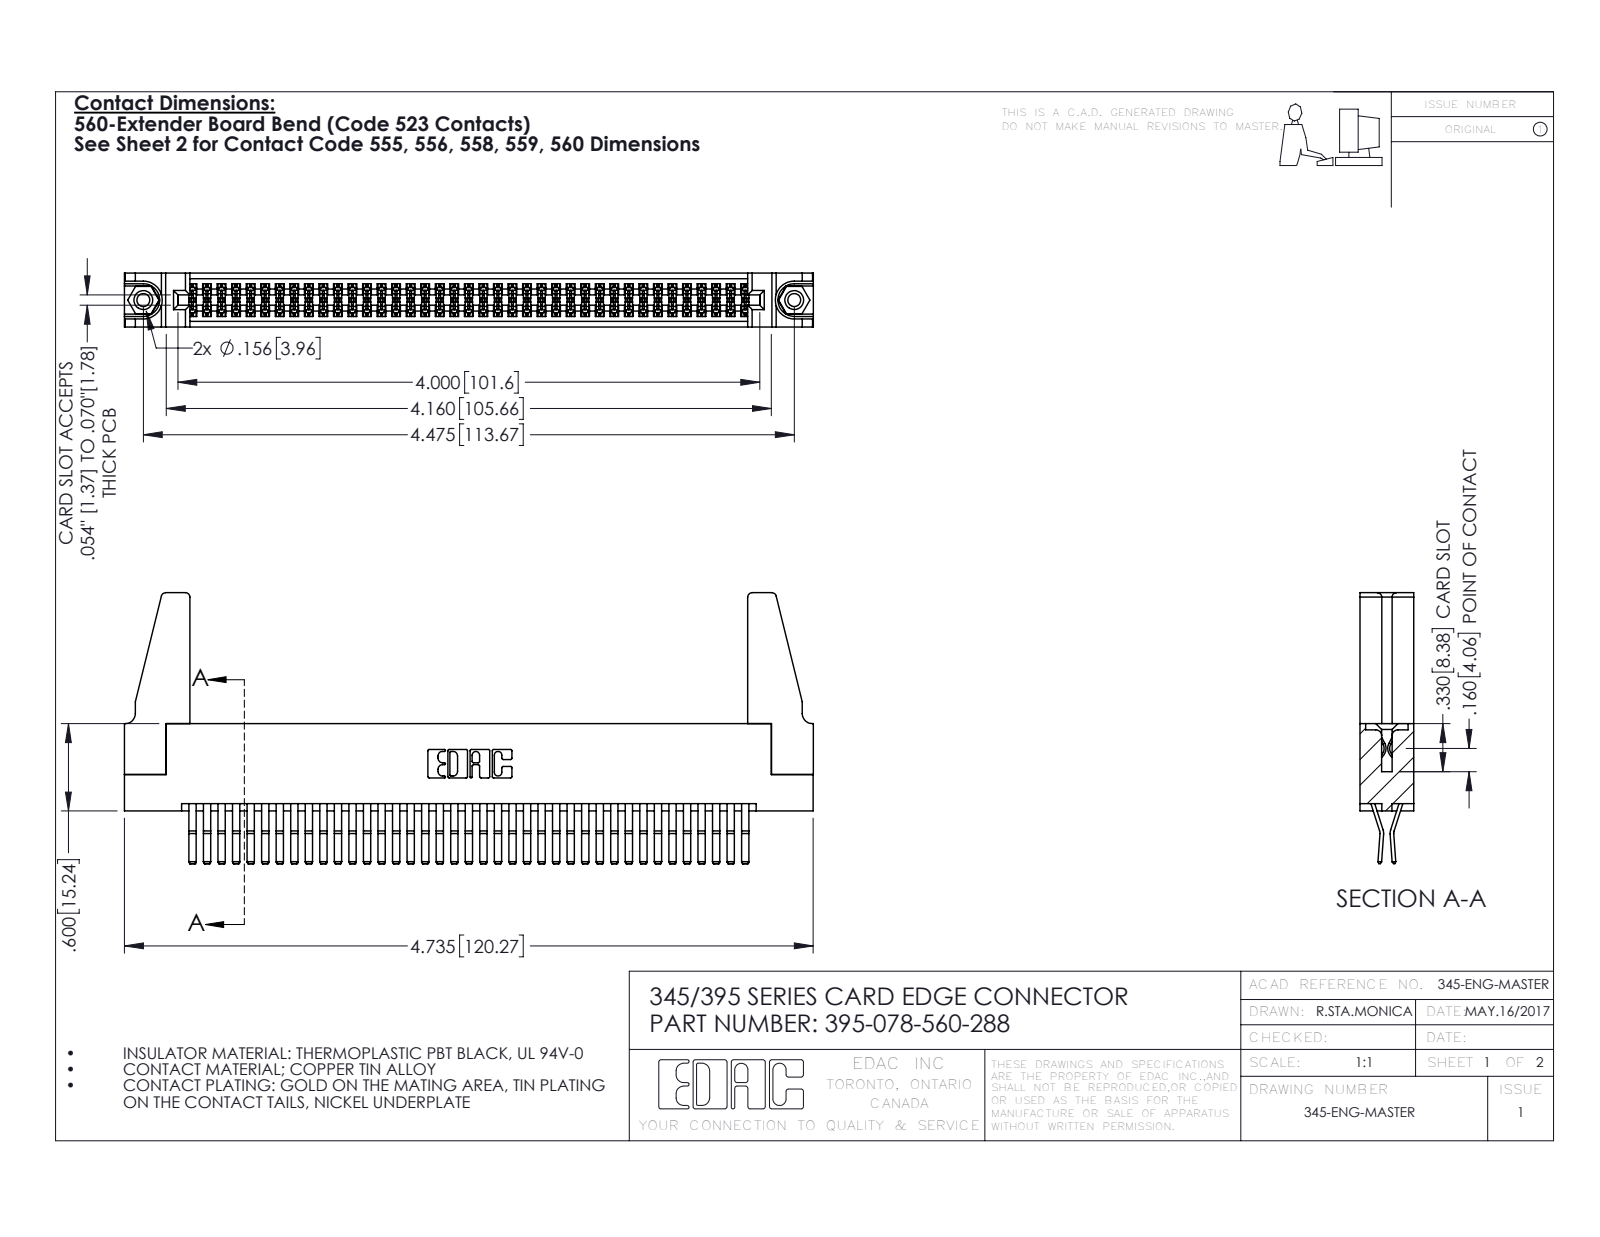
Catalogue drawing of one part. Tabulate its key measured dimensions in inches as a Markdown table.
| quantity | value |
| --- | --- |
| part name | 345 Part_Flush Mounting Lugs - 0.156 Dia-TH; 345-220-078_345-220-088; 395-078-560-288; 345-250-001_345-250-001-102 (+1 more) |
| STEP written by | SolidWorks 2016 (CONFIG_CONTROL_DESIGN) |
| units | inches |
| bodies | 83 solids, 4306 faces (2726 planar, 1564 cylindrical, 16 other) |
| overall size | 4.736 × 1.862 × 0.37 |
| volume | 0.941 in³ |
| surface area | 34.67 in² |
| round holes (diameter × count) | 0.089 × 2, 0.125 × 2, 0.156 × 2, 0.064 × 1 |
| round bosses / shafts (diameter × count) | 0.155 × 2 |
| partial cylindrical surfaces (radius × count) | 0.006 × 117, 0.01 × 22, 0.03 × 8, 0.007 × 6, 0.031 × 6, 0.026 × 3, 0.01 × 2, 0.014 × 2 |
| main face-to-face distances | 0.072, 0.298, 0.025, 0.37, 0.2, 0.098, 0.272, 0.225, 0.175, 0.149 |
| hole center spacings | 0.27, 4.239, 4.475 |
